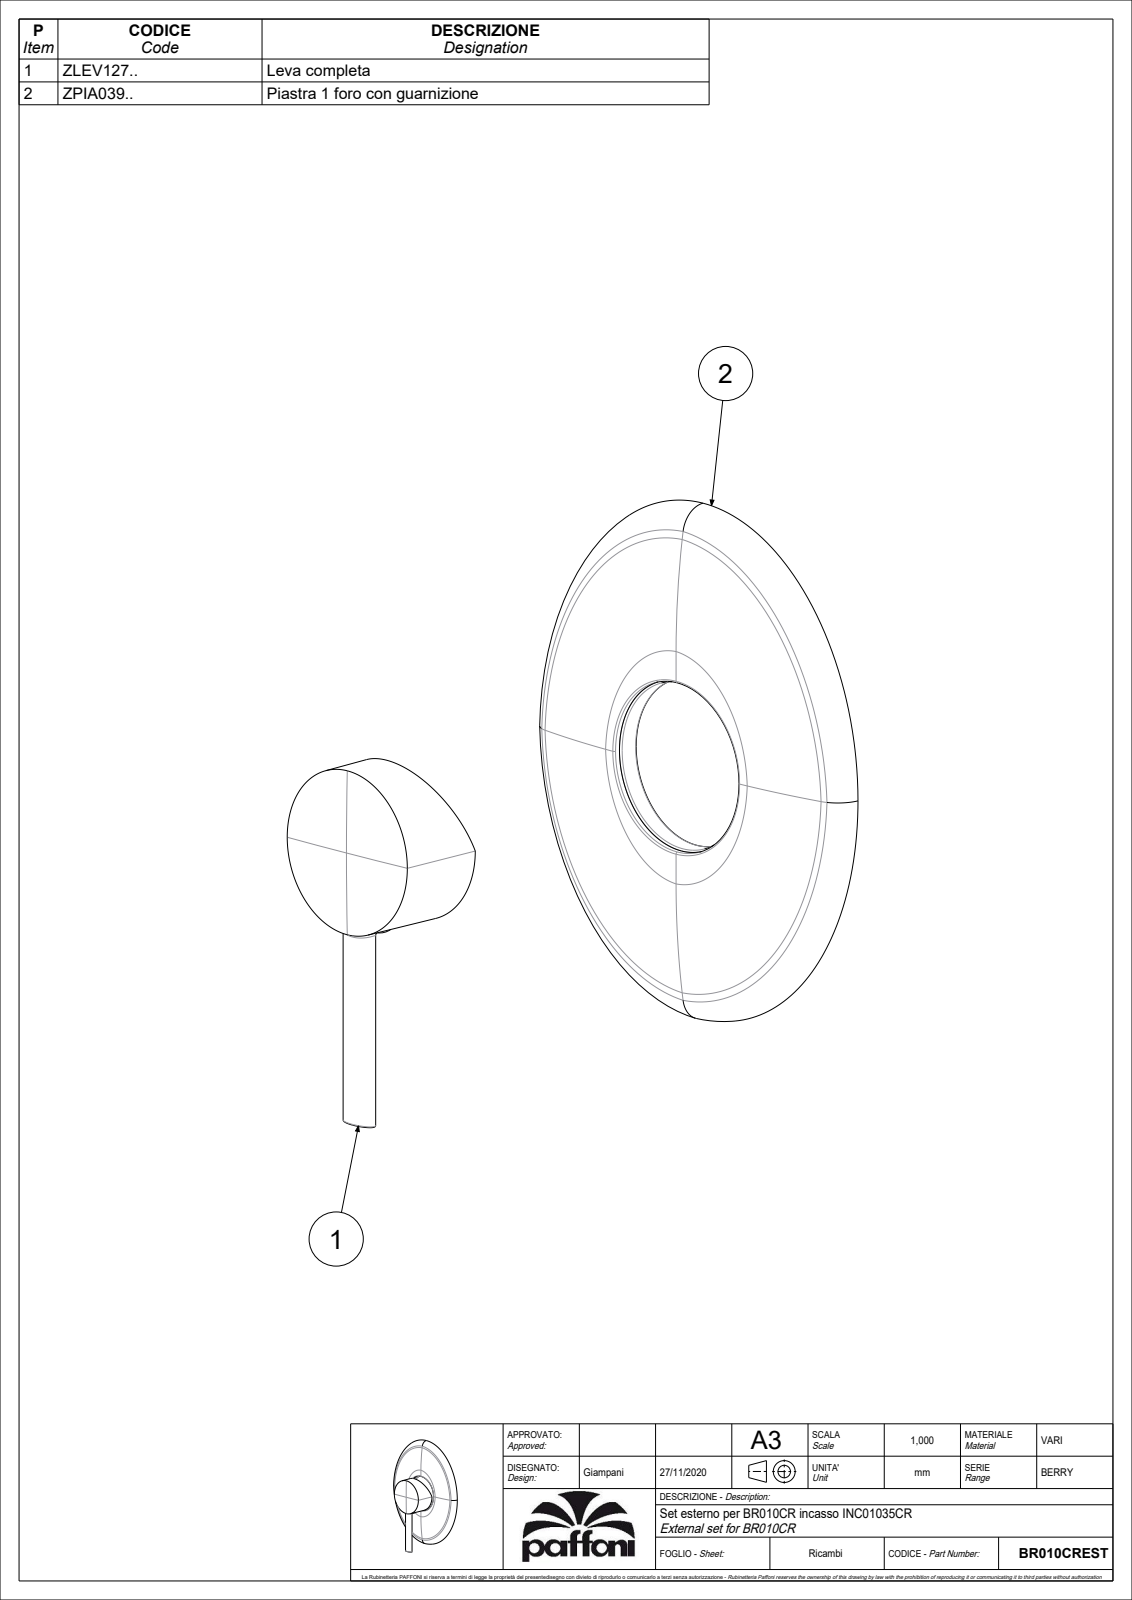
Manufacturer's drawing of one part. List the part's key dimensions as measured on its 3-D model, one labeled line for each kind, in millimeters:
Part name (STEP PRODUCT): BR010CREST
STEP written by: CREO PARAMETRIC BY PTC INC, 2020044 (CONFIG_CONTROL_DESIGN)
Units: millimetres
Bodies: 2 solids, 157 faces (44 planar, 40 cylindrical, 73 other)
Overall size (bounding box): 144.5 × 115 × 37.3
Volume: 41 718 mm³ · Surface area: 38 414 mm²
Round holes (diameter × count): ⌀3 ×1, ⌀3.5 ×1, ⌀7.8 ×1, ⌀45 ×1, ⌀46 ×1
Round bosses / shafts (diameter × count): ⌀51 ×1, ⌀49 ×1, ⌀7.6 ×1, ⌀5.5 ×1
Partial cylindrical surfaces — rounded edges, fillets, slot ends (radius × count): R1.25 ×4, R0.8 ×2, R1 ×2, R1.9 ×1, R2.5 ×1
Main face-to-face distances: 35, 2, 33, 9.1, 0.55, 8.55, 6.87, 15.97, 35.6, 33.6
Hole centre spacings: 0.5
